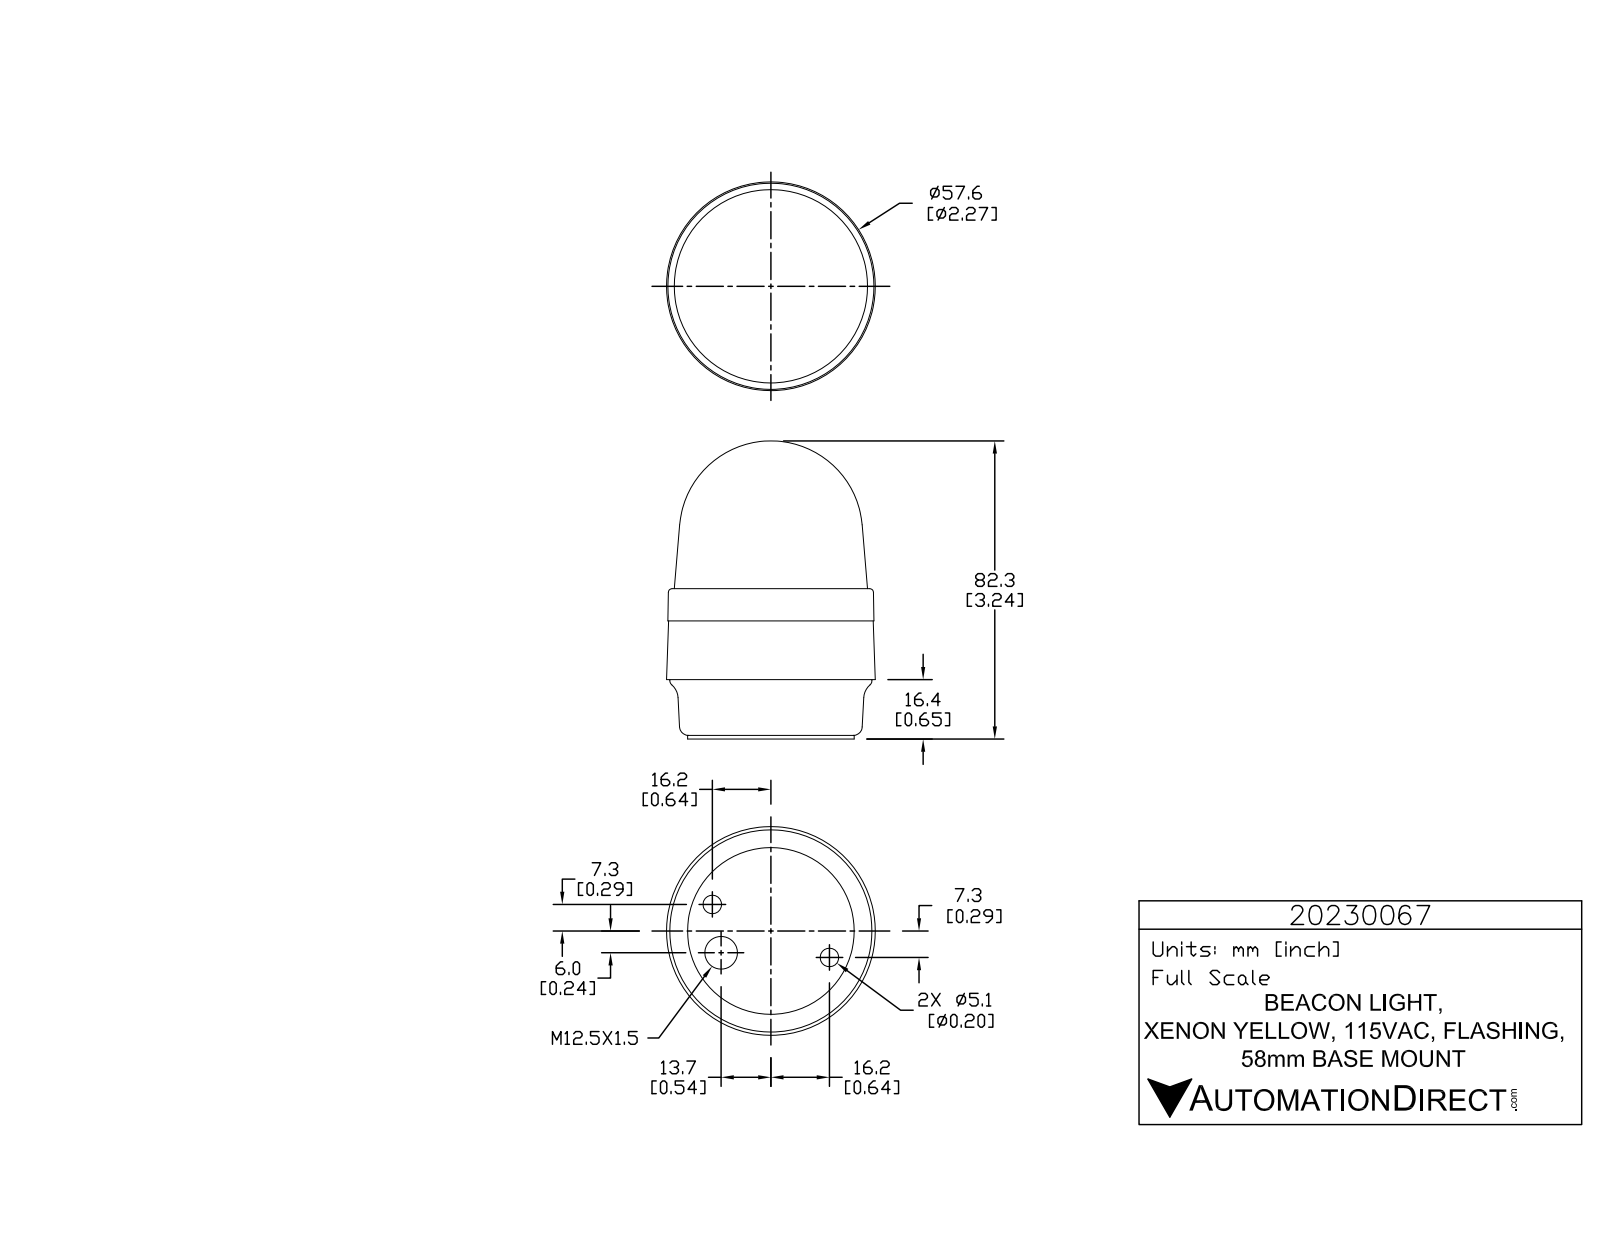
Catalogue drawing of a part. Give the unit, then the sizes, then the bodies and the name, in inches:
Units: inches
Overall size (bounding box): 3.24 × 2.269 × 2.269
Round holes (diameter × count): ⌀0.039 ×3, ⌀0.201 ×2, ⌀0.354 ×1
Round bosses / shafts (diameter × count): ⌀0.226 ×3, ⌀0.056 ×3, ⌀2.197 ×1, ⌀1.811 ×1
Partial cylindrical surfaces — rounded edges, fillets, slot ends (radius × count): R0.008 ×6, R0.008 ×6, R0.008 ×6, R0.131 ×6, R0.004 ×3, R0.005 ×3, R0.007 ×3, R0.008 ×3
Main face-to-face distances: 0.646, 0.039, 0.606, 1.634, 1.594, 0.988, 1.283, 1.244, 0.638, 0.35
Hole centre spacings: 0.534, 1.179, 1.398
Volume: 10.03 in³ · Surface area: 25.2 in²
Bodies: 1 solid, 763 faces (527 planar, 145 cylindrical, 91 other)
Part name (STEP PRODUCT): 20230067
STEP written by: SolidWorks 2015 (AUTOMOTIVE_DESIGN)
